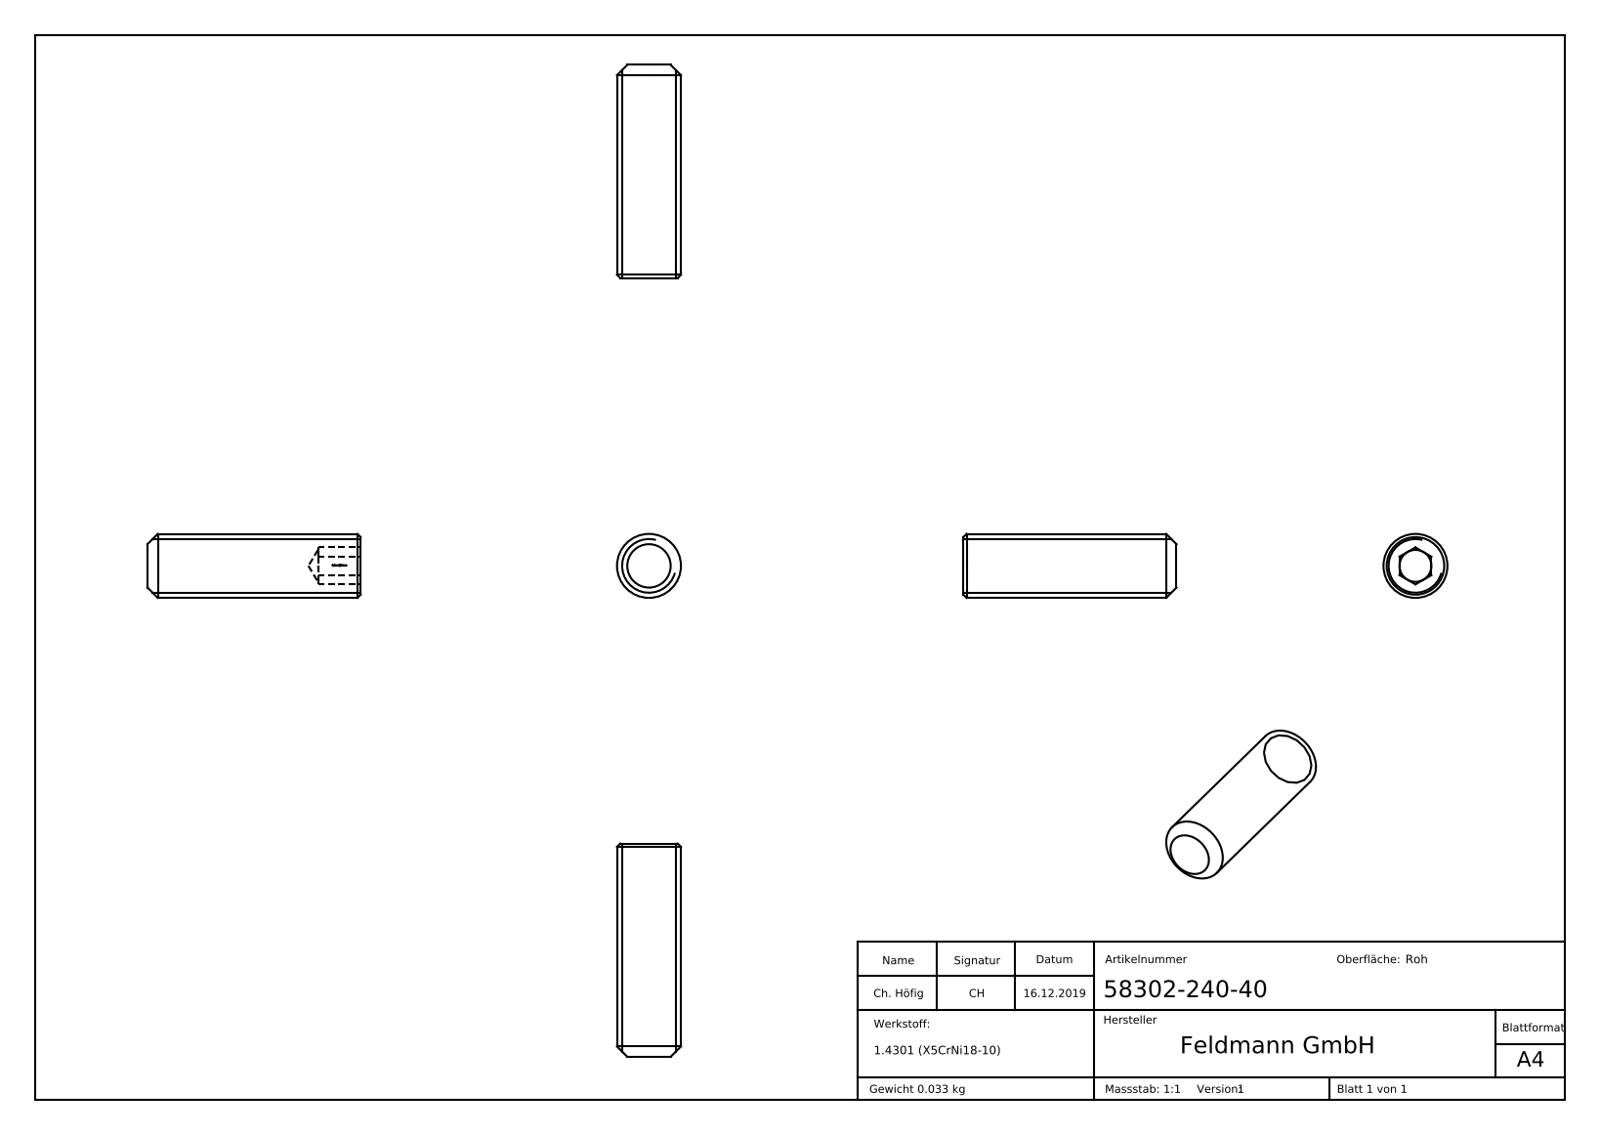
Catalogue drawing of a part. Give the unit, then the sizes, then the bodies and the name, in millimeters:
Units: millimetres
Overall size (bounding box): 91.75 × 12 × 12
Round bosses / shafts (diameter × count): ⌀12 ×1
Main face-to-face distances: 6, 40, 32, 8, 6.1, 0.48, 0.54, 0.31, 0.34, 0.36
Volume: 4 188 mm³ · Surface area: 1 845 mm²
Bodies: 1 solid, 297 faces (151 planar, 1 cylindrical, 145 other)
Part name (STEP PRODUCT): 58302-240-40
STEP written by: SolidWorks 2015 (CONFIG_CONTROL_DESIGN)
